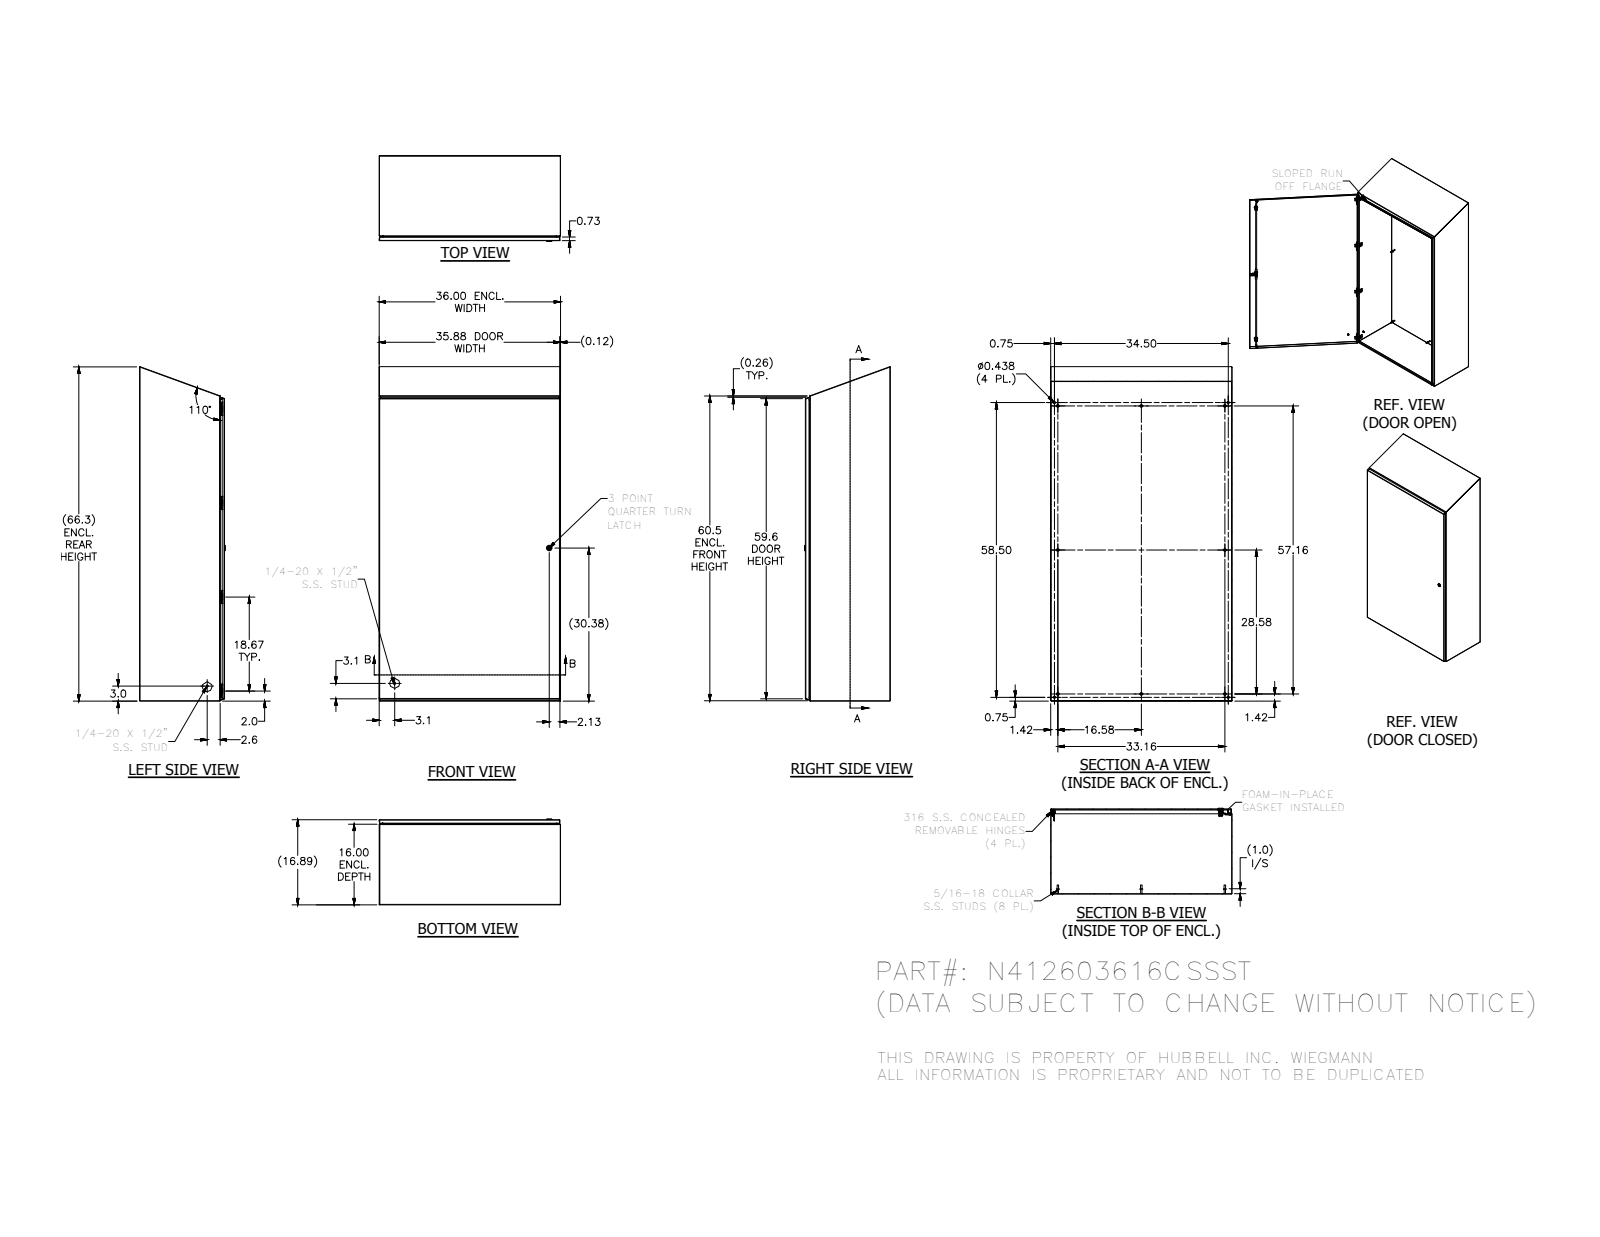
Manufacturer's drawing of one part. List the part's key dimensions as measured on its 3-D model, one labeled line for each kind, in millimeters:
Part name (STEP PRODUCT): N412_CSSST-assm3pcblr; N412603616CSSSTBLR; HFW3161; HFW328176 (+8 more)
STEP written by: Autodesk Inventor 2012 (AUTOMOTIVE_DESIGN)
Units: millimetres
Bodies: 82 solids, 2675 faces (981 planar, 996 cylindrical, 698 other)
Overall size (bounding box): 1686 × 914.4 × 432.9
Volume: 9 994 000 mm³ · Surface area: 10 620 000 mm²
Round holes (diameter × count): ⌀2.4 ×8, ⌀3.9 ×8, ⌀4.2 ×8, ⌀4.4 ×8, ⌀4.7 ×8, ⌀4 ×5, ⌀5 ×5, ⌀4.2 ×4, ⌀11.1 ×4, ⌀2.7 ×2, ⌀4.1 ×2, ⌀4.3 ×2
Round bosses / shafts (diameter × count): ⌀6.4 ×18, ⌀14.3 ×8, ⌀9.1 ×8, ⌀8.1 ×8, ⌀7.6 ×8, ⌀7 ×8, ⌀6.5 ×8, ⌀4.2 ×8
Partial cylindrical surfaces — rounded edges, fillets, slot ends (radius × count): R1.3 ×50, R0.4 ×34, R0.8 ×33, R3.2 ×32, R0.3 ×30, R0.5 ×20, R0.8 ×16, R3 ×16
Main face-to-face distances: 1.9, 427.1, 425.2, 428.9, 912.5, 910.6, 914.4, 404.5, 22.5, 20.7
Hole centre spacings: 474.1, 948.3, 474.1, 1422.4, 12.7, 16.7, 33.2, 474.3
